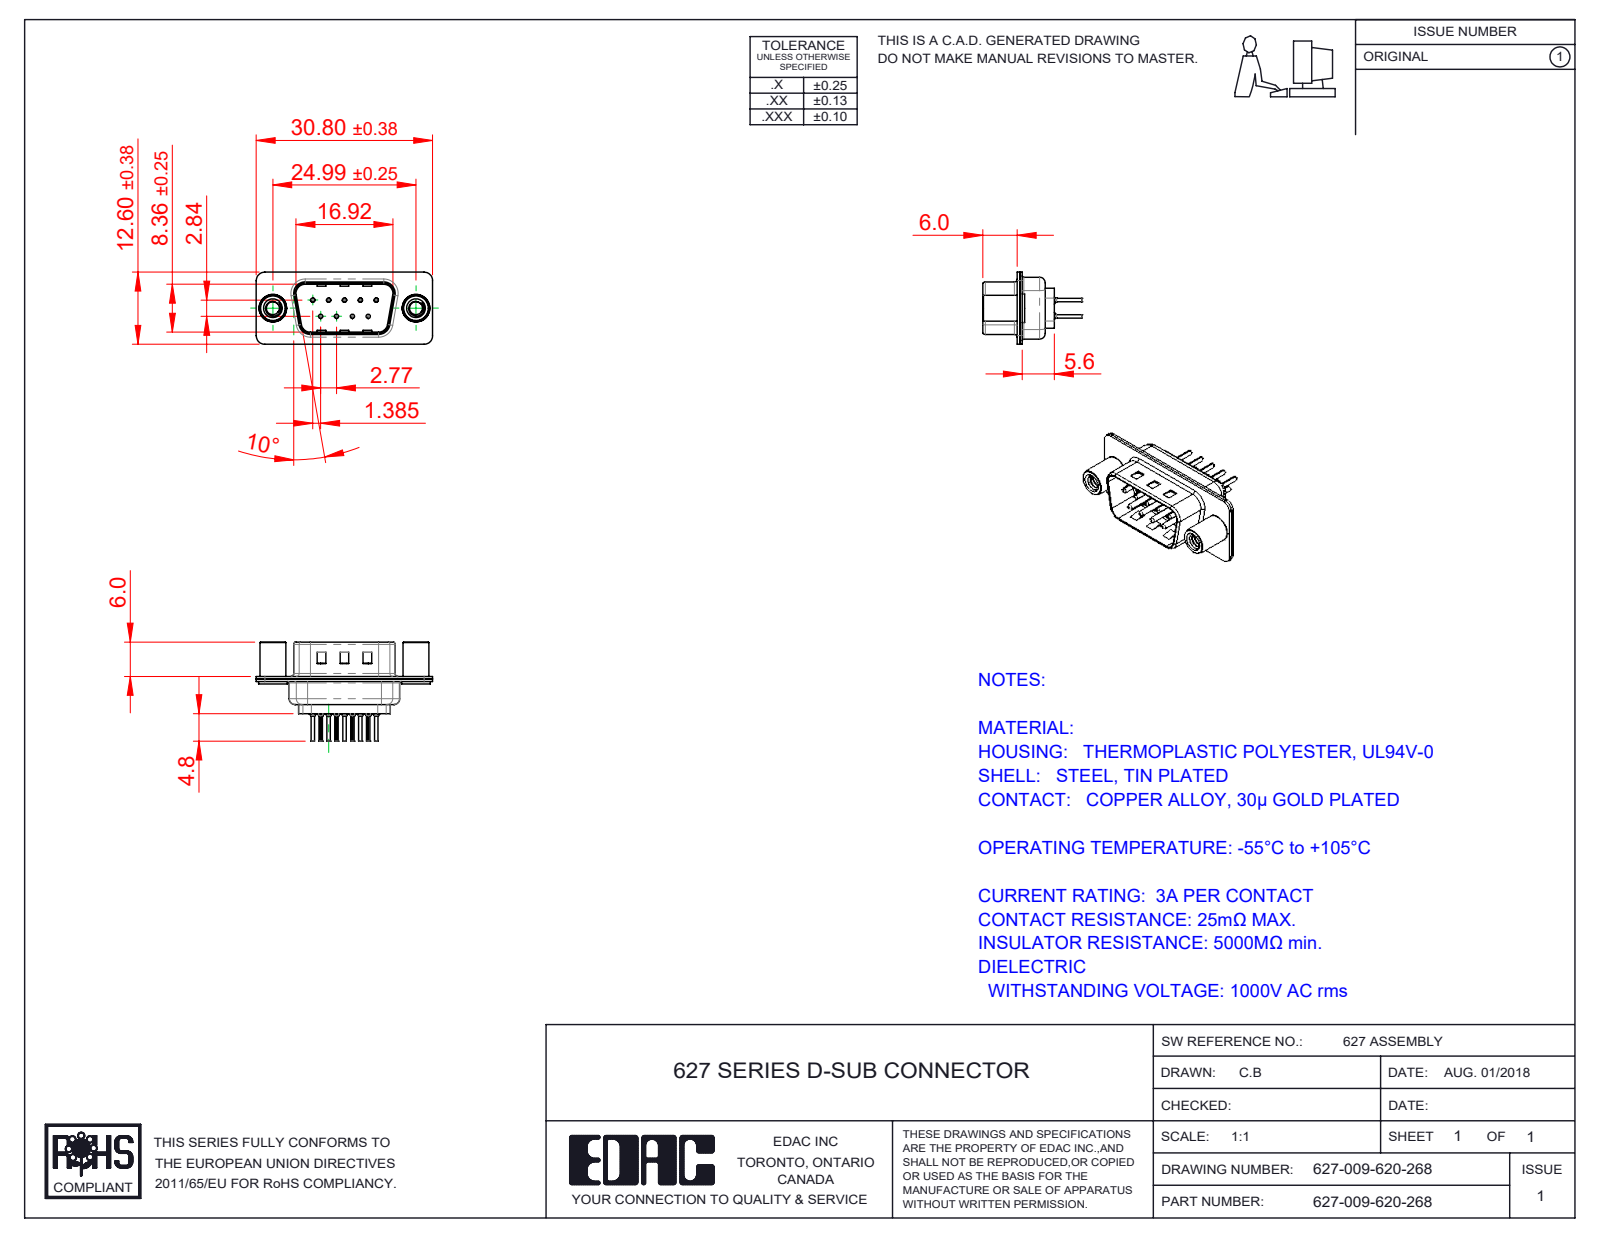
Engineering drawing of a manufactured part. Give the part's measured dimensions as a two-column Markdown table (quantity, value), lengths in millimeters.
| quantity | value |
| --- | --- |
| part name | 627 4-40 Threaded Standoff; 627 Shell Front_09 Contacts; 627-009-620-068; 627 Contact Row 1_20L (+3 more) |
| STEP written by | SolidWorks 2020 (CONFIG_CONTROL_DESIGN) |
| units | millimeters |
| bodies | 14 solids, 1220 faces (325 planar, 490 cylindrical, 405 other) |
| overall size | 30.8 × 17.3 × 12.6 |
| volume | 1 375 mm³ |
| surface area | 4 129 mm² |
| round holes (diameter × count) | 0.2 × 9, 0.35 × 9, 1.1 × 9, 1.6 × 9, 2.26 × 2, 4 × 2, 4.8 × 2 |
| round bosses / shafts (diameter × count) | 2 × 9, 1.5 × 9, 0.75 × 9, 0.6 × 9, 5 × 2, 4.9 × 2, 4.5 × 2 |
| partial cylindrical surfaces (radius × count) | 0.1 × 18, 1.5 × 18, 2 × 12, 0.5 × 8, 1.6 × 8, 0.25 × 4, 0.6 × 4, 0.65 × 4 |
| main face-to-face distances | 0.4, 0.45, 0.9, 0.82, 9.58, 1.4, 8.76, 0.5, 1.5, 5.6 |
| hole center spacings | 3.16, 2.77, 5.54, 5.03, 5.04, 8.31, 7.48, 7.49 |
